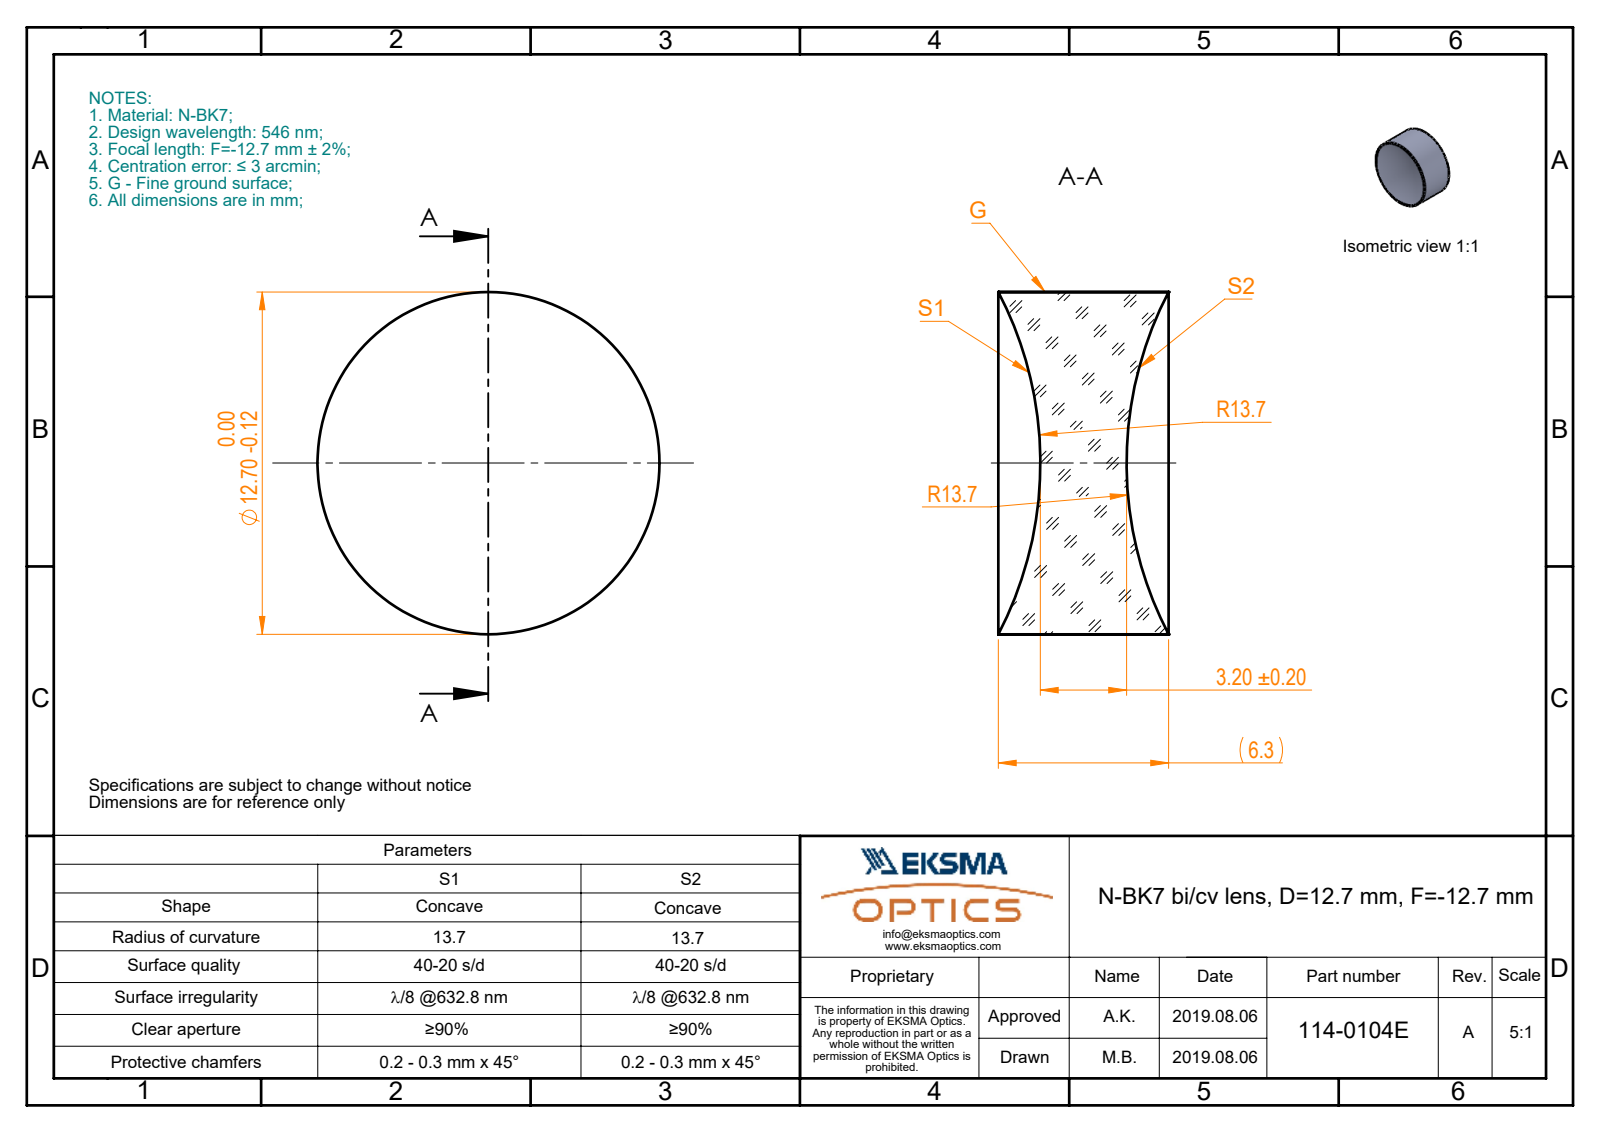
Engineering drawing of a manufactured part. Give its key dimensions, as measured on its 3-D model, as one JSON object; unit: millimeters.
{"part_name": "114-0104E BK7 bi-cv 12.7 F-12.7", "step_written_by": "SolidWorks 2017 (CONFIG_CONTROL_DESIGN)", "units": "millimeters", "bodies": {"solids": 1, "faces": 6, "planar": 0, "cylindrical": 2, "other": 4}, "overall_size": [12.7, 12.7, 6.32], "volume_mm3": 599, "surface_area_mm2": 521, "round_bosses_or_shafts": [[12.7, 1]]}
